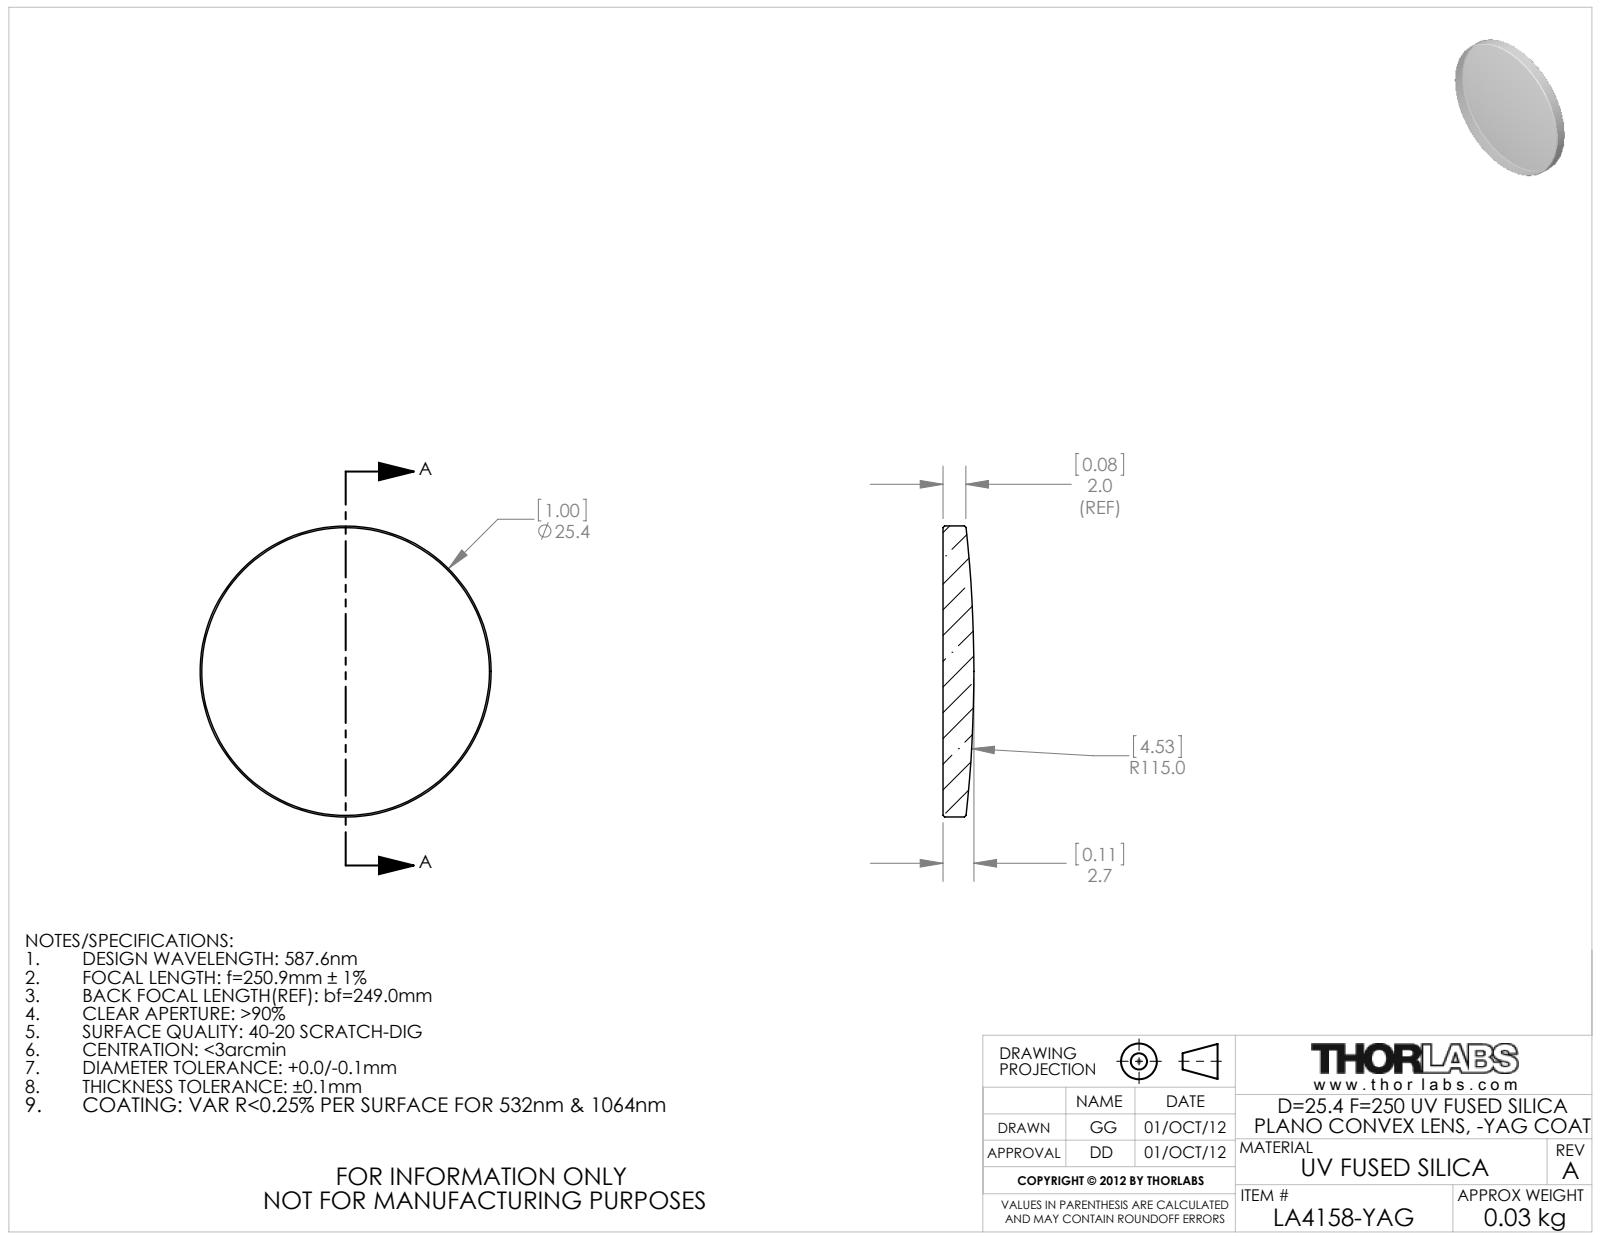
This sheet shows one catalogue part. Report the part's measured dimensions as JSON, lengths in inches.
{"part_name": "24958-E0W", "step_written_by": "SolidWorks 2011 (CONFIG_CONTROL_DESIGN)", "units": "inches", "bodies": {"solids": 1, "faces": 9, "planar": 1, "cylindrical": 2, "other": 6}, "overall_size": [1, 1, 0.106], "volume_in3": 0.073, "surface_area_in2": 1.801, "round_bosses_or_shafts": [[1, 1]]}
